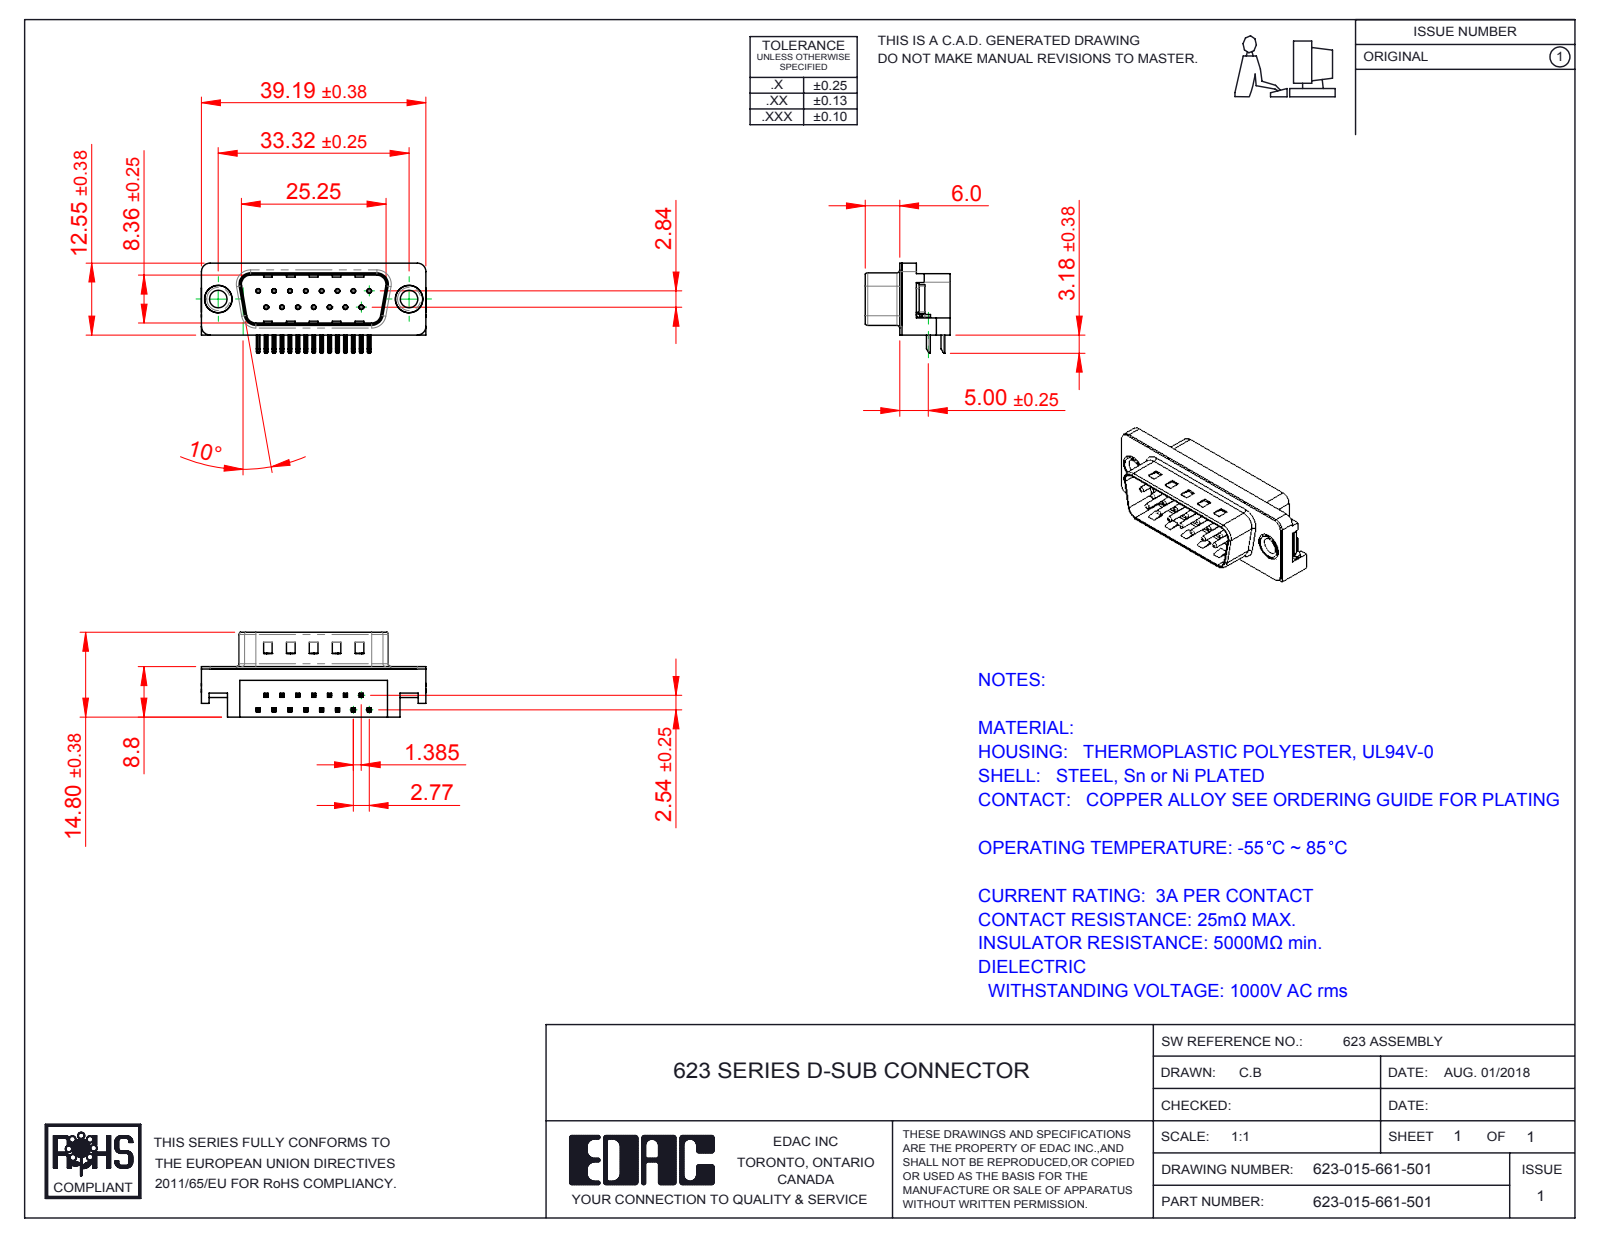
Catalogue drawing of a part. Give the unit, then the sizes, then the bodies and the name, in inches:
Units: inches
Overall size (bounding box): 1.544 × 0.619 × 0.583
Round holes (diameter × count): ⌀0.014 ×15, ⌀0.031 ×15, ⌀0.12 ×2, ⌀0.157 ×2, ⌀0.189 ×2, ⌀0.197 ×2
Round bosses / shafts (diameter × count): ⌀0.03 ×15, ⌀0.193 ×2, ⌀0.187 ×2, ⌀0.152 ×2
Partial cylindrical surfaces — rounded edges, fillets, slot ends (radius × count): R0.01 ×68, R0.005 ×30, R0.039 ×16, R0.02 ×9, R0.059 ×6, R0.035 ×4, R0.063 ×4, R0.079 ×4
Main face-to-face distances: 0.016, 0.331, 0.083, 0.067, 0.346, 0.412, 0.428, 0.345, 0.232, 0.114
Hole centre spacings: 0.124, 0.109, 0.218, 0.327, 0.436, 0.198, 0.198, 0.294
Volume: 0.202 in³ · Surface area: 7.535 in²
Bodies: 21 solids, 1427 faces (893 planar, 417 cylindrical, 117 other)
Part name (STEP PRODUCT): 623 Contact Top; 623 Thru Hole Rivet; 623 Shell_15 Socket; 623 Non Board Mount (+3 more)
STEP written by: SolidWorks 2016 (CONFIG_CONTROL_DESIGN)
